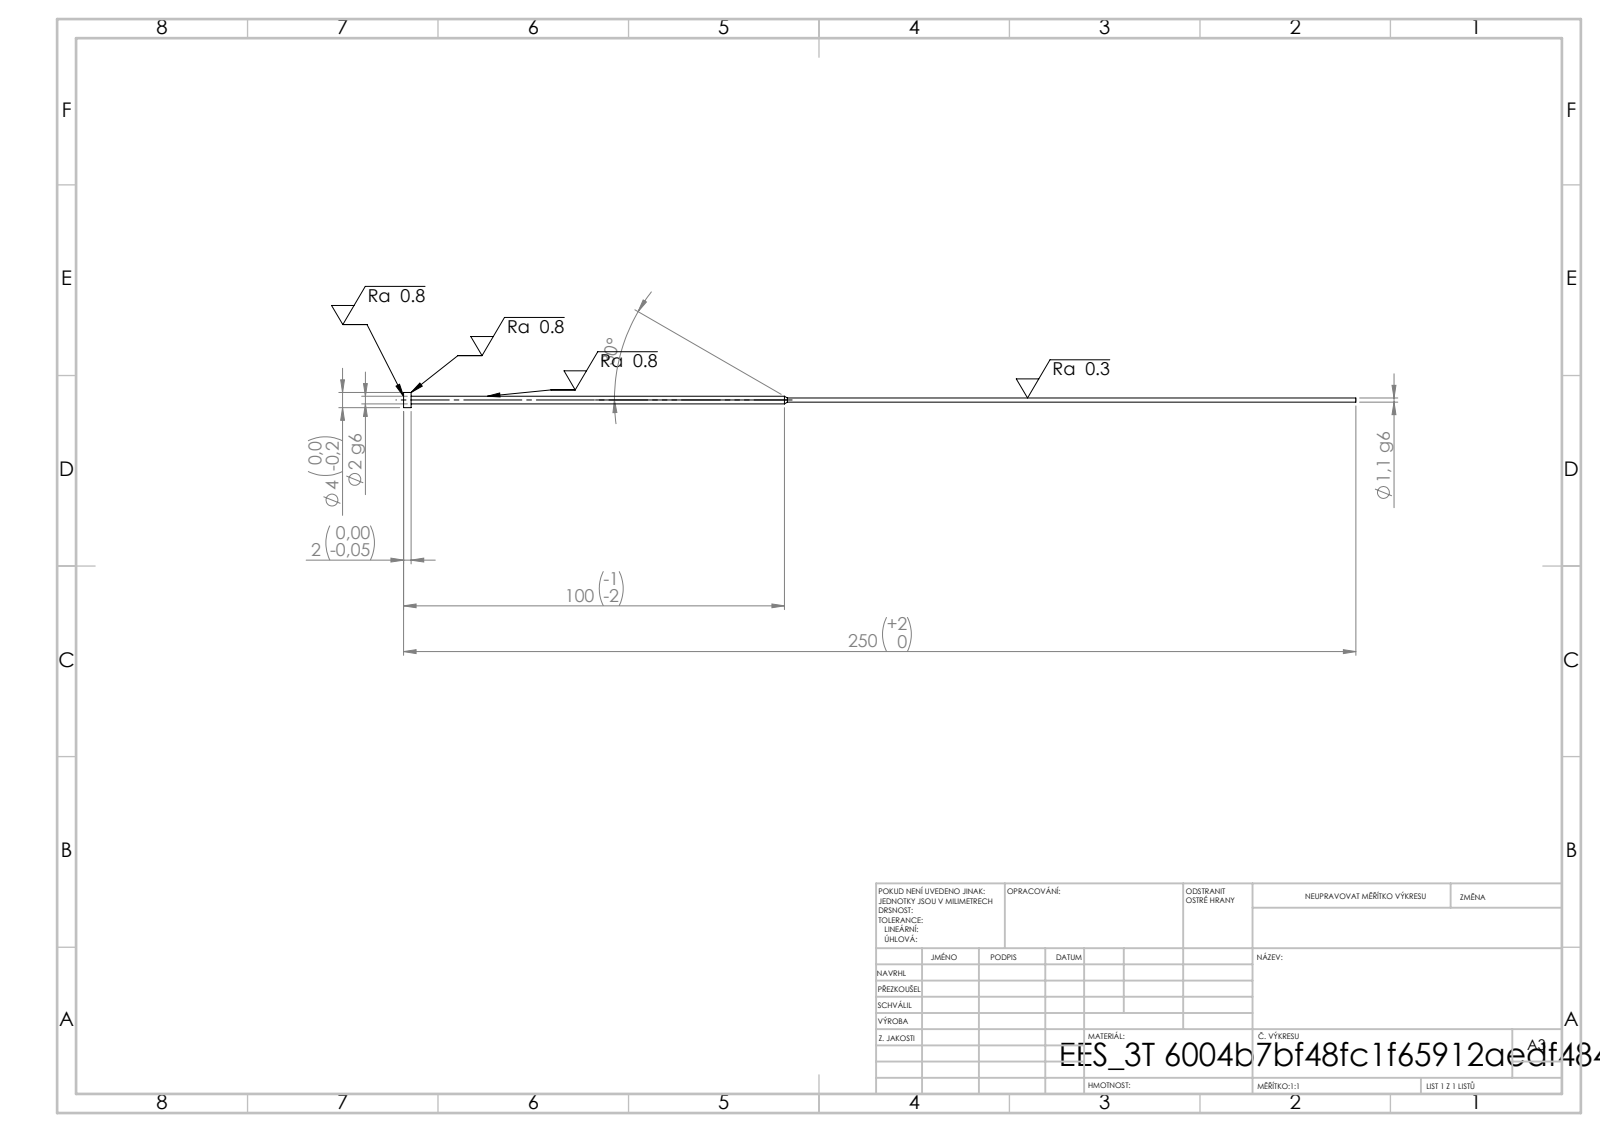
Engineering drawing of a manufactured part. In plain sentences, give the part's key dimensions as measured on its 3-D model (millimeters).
Its 3-D file was written by "SolidWorks 2019 (CONFIG_CONTROL_DESIGN)". It is 1 solid with 11 faces: 3 planar, 6 cylindrical and 2 other. Overall it measures 250 by 4 by 4 millimeters. Its volume is 476 cubic millimeters and its surface area 1 184 square millimeters. Round bosses or shafts: 1 of diameter 4, 1 of diameter 2, 1 of diameter 1.1. The main face-to-face distances are 2, 248, 250.
